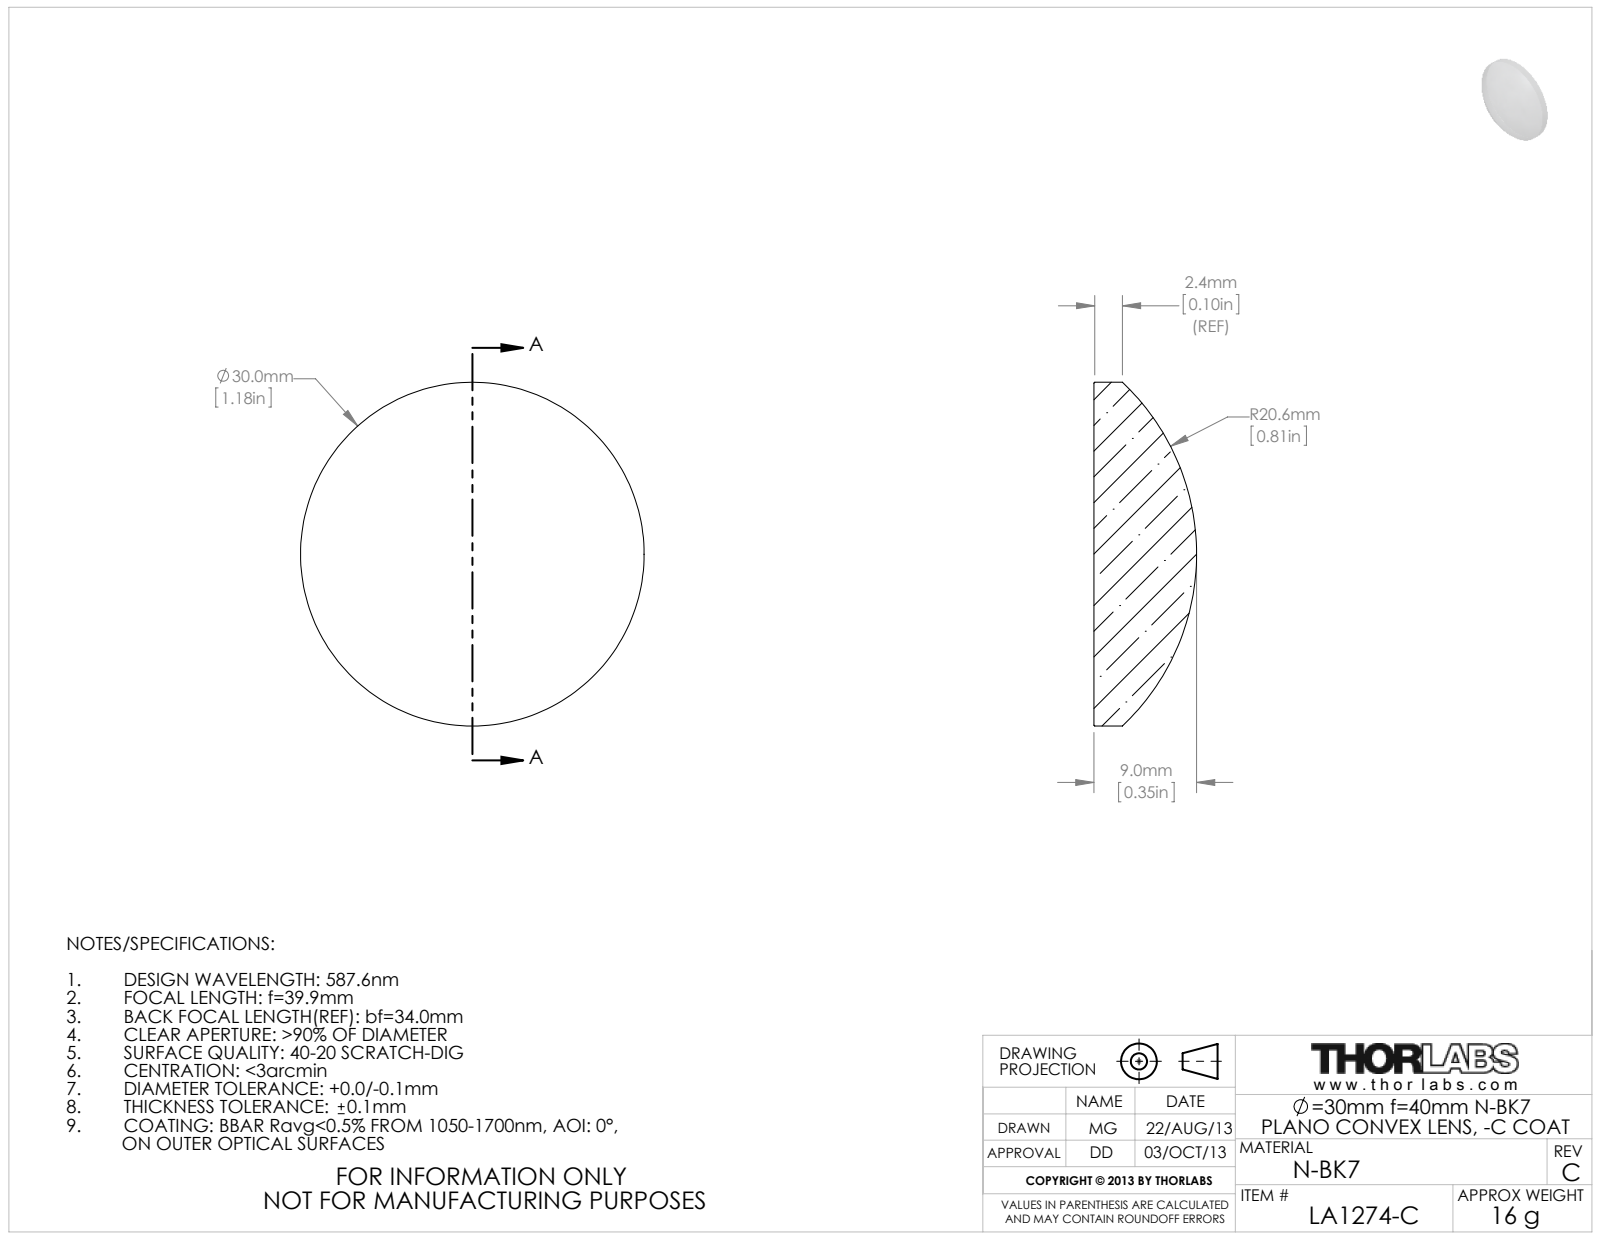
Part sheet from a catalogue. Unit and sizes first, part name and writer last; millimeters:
Units: millimetres
Overall size (bounding box): 30 × 30 × 8.97
Round bosses / shafts (diameter × count): ⌀30 ×1
Volume: 4 193 mm³ · Surface area: 1 780 mm²
Bodies: 1 solid, 5 faces (1 planar, 2 cylindrical, 2 other)
Part name (STEP PRODUCT): 4595-E0W
STEP written by: SolidWorks 2009 (AUTOMOTIVE_DESIGN)
